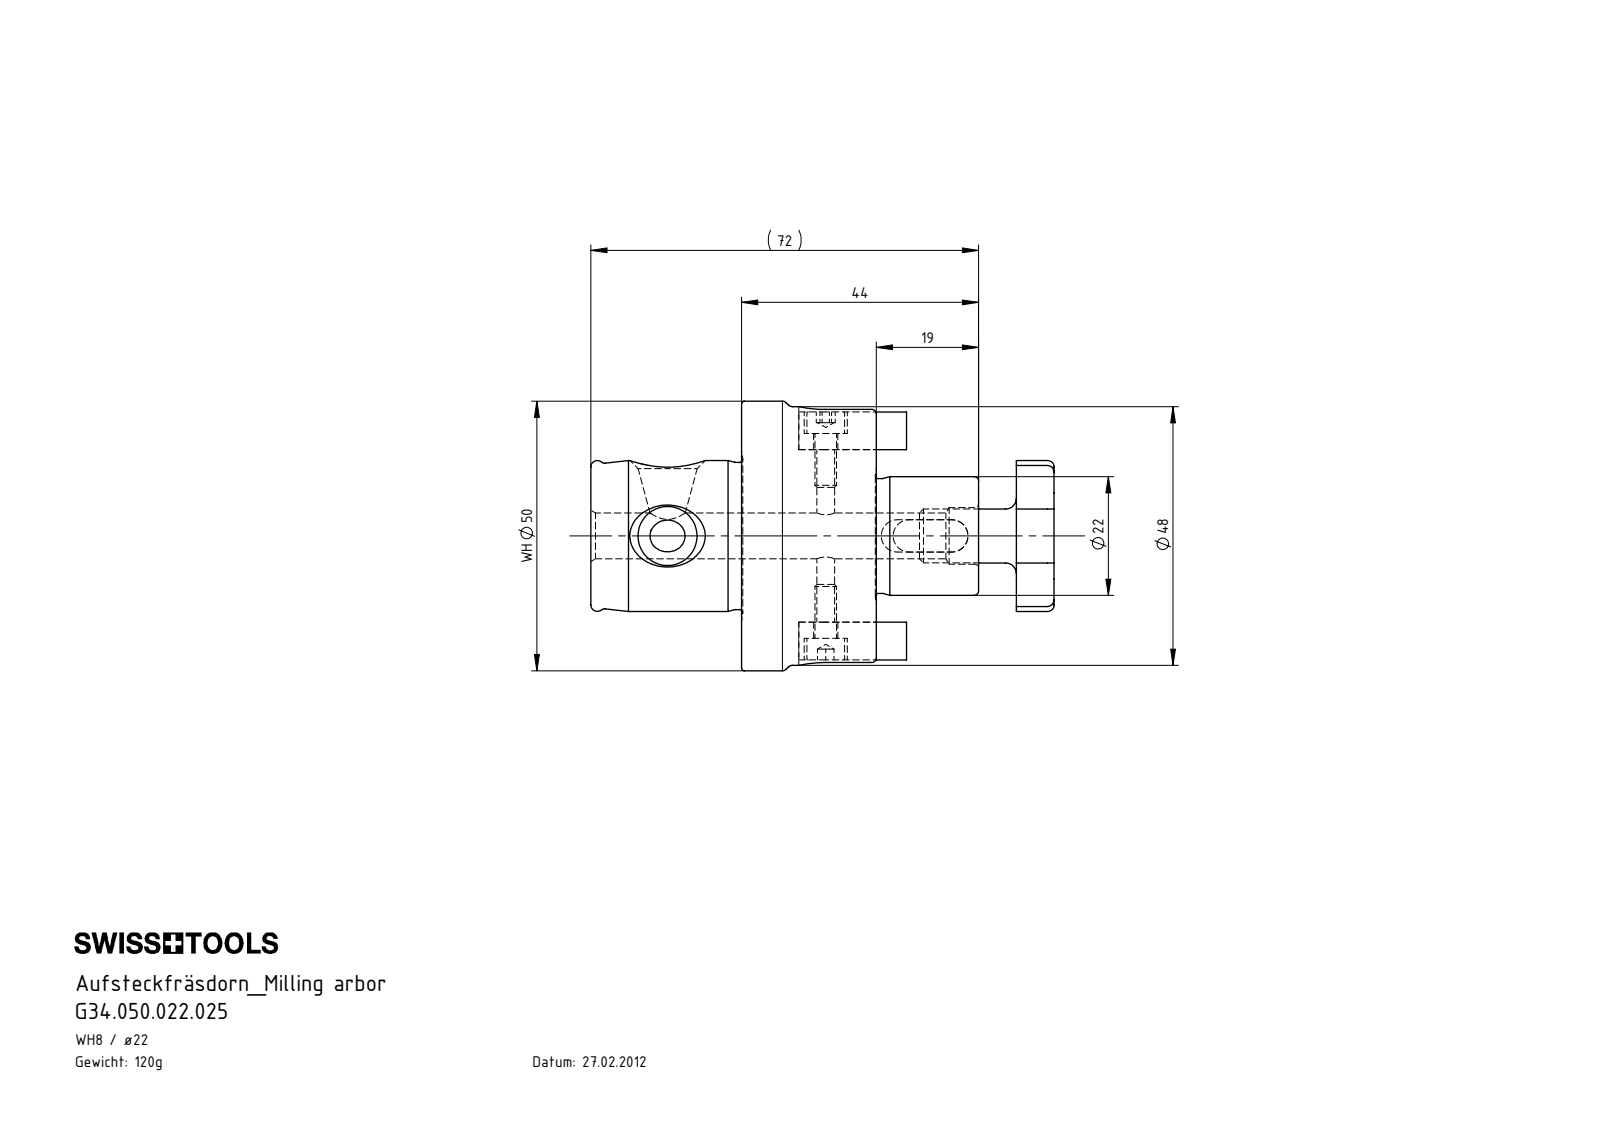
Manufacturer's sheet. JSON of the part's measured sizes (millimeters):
{"part_name": "ISO 4762 - M4 x 10_PreviewCfg; D22-ER2.002.010_A; WH5.D22.001.025; WH5-D22.001.025 (+2 more)", "step_written_by": "SolidWorks 2022 (AUTOMOTIVE_DESIGN)", "units": "millimeters", "bodies": {"solids": 7, "faces": 207, "planar": 70, "cylindrical": 58, "other": 79}, "overall_size": [86, 50, 50], "volume_mm3": 70176, "surface_area_mm2": 18982, "round_holes": [[3.3, 1], [4.5, 1], [8, 1], [8.5, 1], [10.5, 1]], "round_bosses_or_shafts": [[50, 1], [48, 1], [28, 1], [27.3, 1], [22, 1], [21.3, 1], [10, 1], [7, 1]], "partial_cylinders_radius": [[3, 7], [5, 1]], "face_to_face_distances": [25, 7, 28, 10, 26, 33, 53, 86, 58, 19]}
